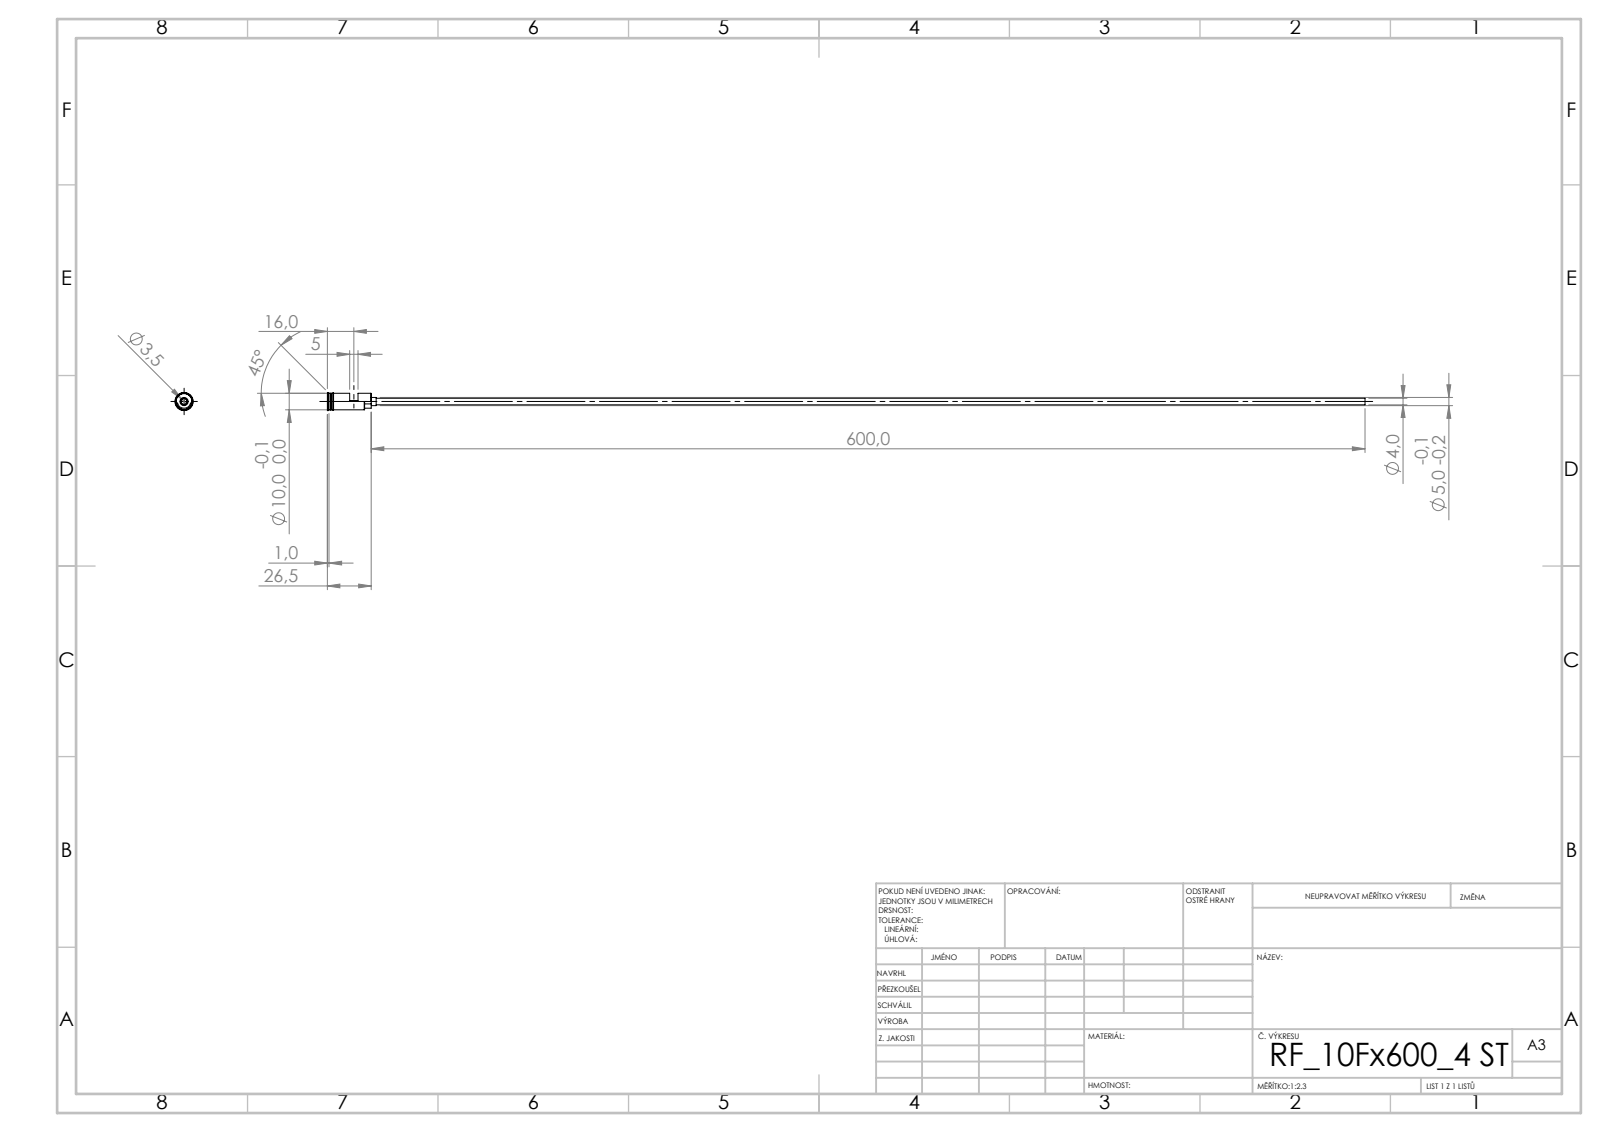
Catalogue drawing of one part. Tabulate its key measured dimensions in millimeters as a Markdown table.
| quantity | value |
| --- | --- |
| STEP written by | SolidWorks 2019 (CONFIG_CONTROL_DESIGN) |
| units | millimeters |
| bodies | 1 solid, 55 faces (24 planar, 19 cylindrical, 12 other) |
| overall size | 626.5 × 11 × 11 |
| volume | 3 494 mm³ |
| surface area | 15 350 mm² |
| round holes (diameter × count) | 3.5 × 1 |
| round bosses / shafts (diameter × count) | 11 × 1, 10 × 1, 9.8 × 1, 5 × 1, 4 × 1 |
| partial cylindrical surfaces (radius × count) | 3 × 2, 4.05 × 1 |
| main face-to-face distances | 26.5, 13, 13.5, 24.5, 11.5, 2, 8, 5, 16.5, 18.5 |
